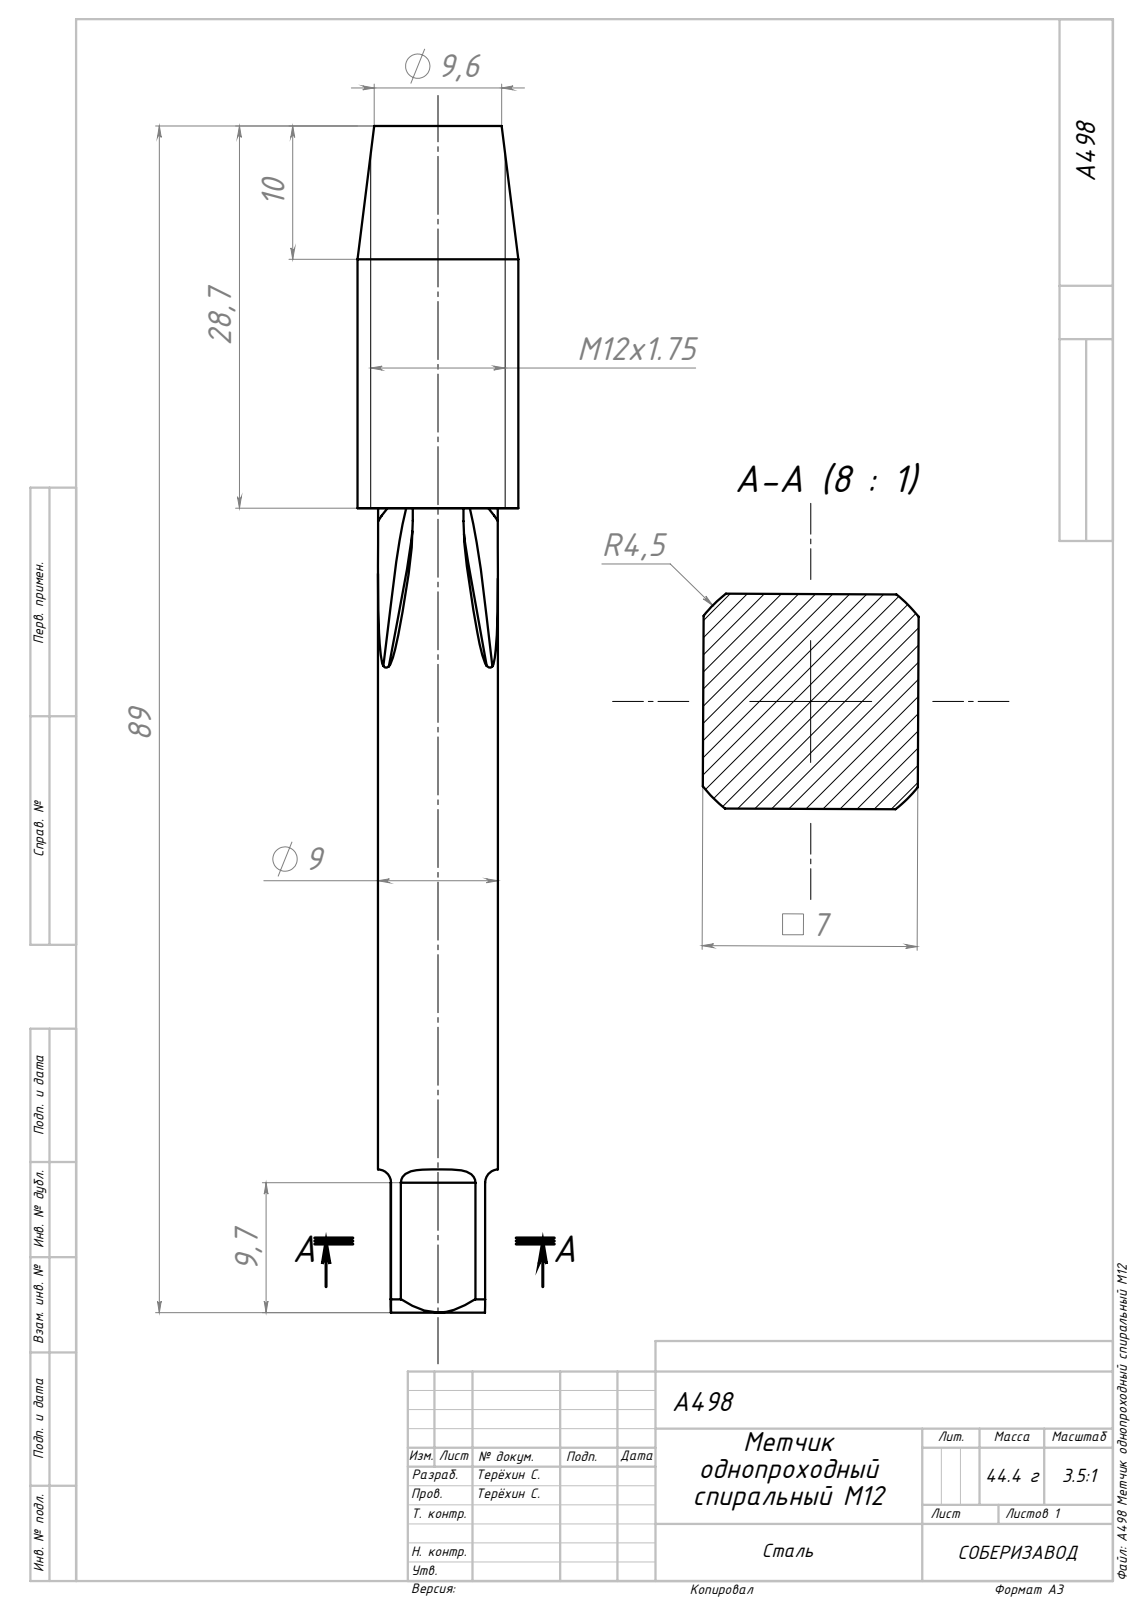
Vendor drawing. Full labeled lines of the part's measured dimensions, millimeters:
Part name (STEP PRODUCT): A498 Метчик однопроходный спиральный М12
STEP written by: SolidWorks 2021 (AUTOMOTIVE_DESIGN)
Units: millimetres
Bodies: 1 solid, 292 faces (10 planar, 85 cylindrical, 197 other)
Overall size (bounding box): 89 × 12.1 × 11.39
Volume: 4 862 mm³ · Surface area: 3 317 mm²
Round holes (diameter × count): ⌀1.6 ×1
Round bosses / shafts (diameter × count): ⌀9 ×1
Partial cylindrical surfaces — rounded edges, fillets, slot ends (radius × count): R4.46 ×24, R4.5 ×6, R1 ×4
Main face-to-face distances: 7.06, 89, 2, 87
